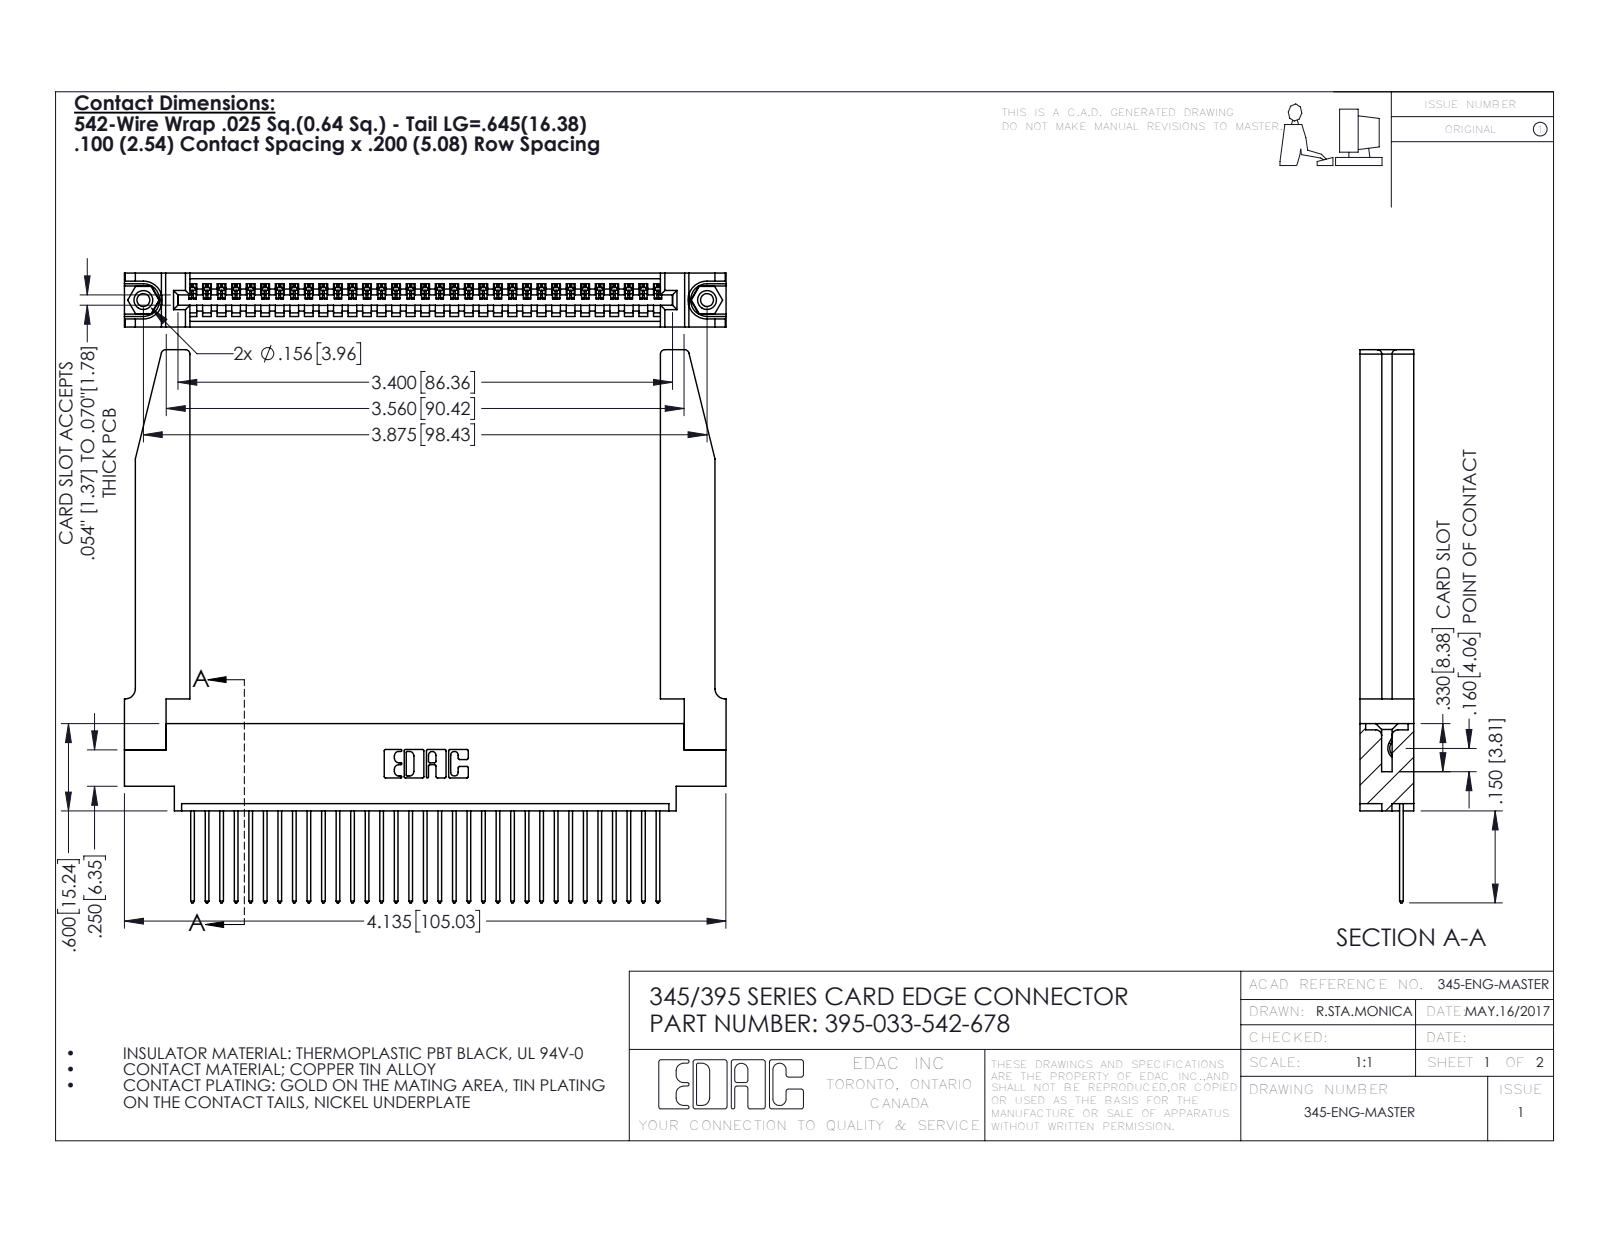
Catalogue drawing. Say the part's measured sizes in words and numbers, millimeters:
The part is named "345-220-078_345-220-078; 345-292-001_345-293-142; 395-033-542-678; 345 Part_0.170 Offset - 0.156 Dia-TH (+1 more)". Its 3-D file was written by "SolidWorks 2016 (CONFIG_CONTROL_DESIGN)". It is 38 solids with 2278 faces: 1546 planar, 680 cylindrical and 52 other. Overall it measures 105.1 by 96.6 by 9.4 millimeters. Its volume is 17 630 cubic millimeters and its surface area 20 430 square millimeters. Round holes: 2 of diameter 2.3, 2 of diameter 3.2, 2 of diameter 4, 1 of diameter 1.6. Round bosses or shafts: 2 of diameter 3.9. Partial cylindrical surfaces (rounded edges, fillets, slot ends): 66 of radius 0.2, 66 of radius 0.3, 22 of radius 0.3, 8 of radius 0.8, 6 of radius 0.2, 6 of radius 0.8, 3 of radius 0.7, 2 of radius 0.8. The main face-to-face distances are 9.4, 1.8, 7.6, 2.5, 6.9, 0.6, 5.1, 3.8, 3.8, 5.7. The hole center spacings are 6.9, 92.5, 98.4.
